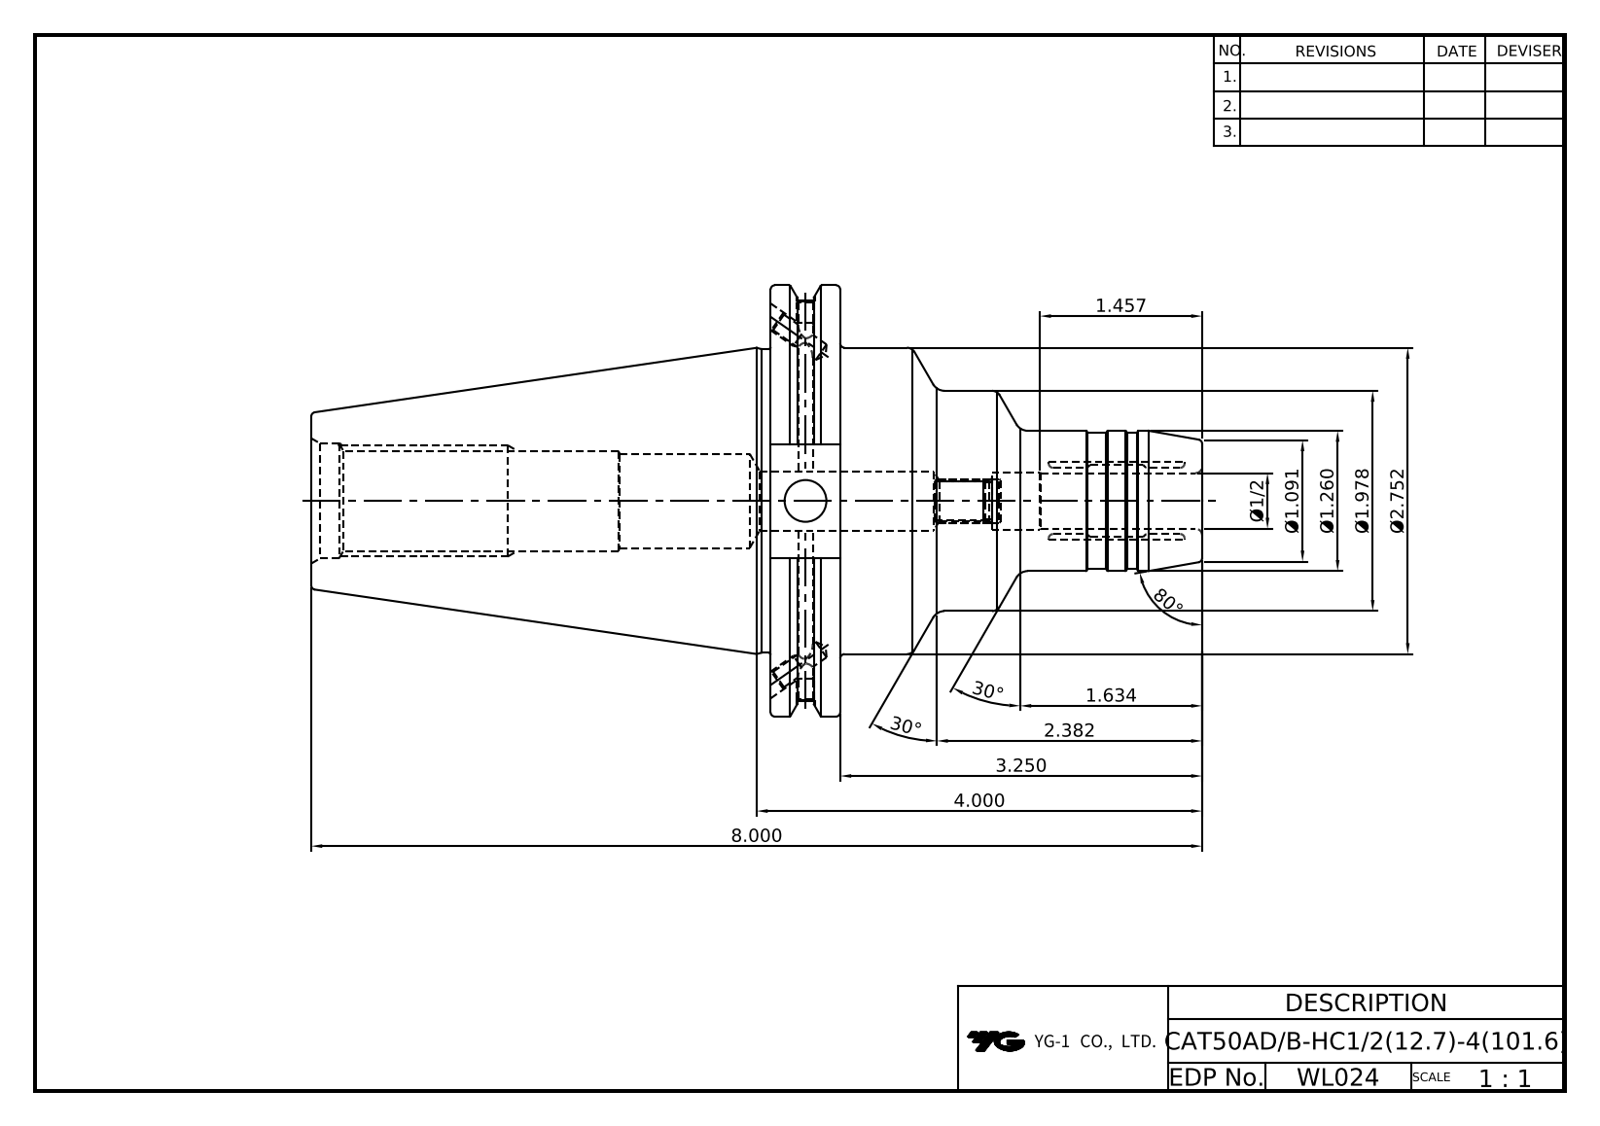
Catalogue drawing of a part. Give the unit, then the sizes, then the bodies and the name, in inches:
Units: inches
Overall size (bounding box): 8 × 3.875 × 3.728
Round holes (diameter × count): ⌀0.128 ×2, ⌀0.163 ×2, ⌀0.165 ×2, ⌀0.197 ×2, ⌀0.351 ×1, ⌀0.375 ×1, ⌀0.5 ×1, ⌀0.52 ×1, ⌀0.531 ×1, ⌀0.807 ×1, ⌀0.865 ×1, ⌀1.031 ×1
Round bosses / shafts (diameter × count): ⌀3.875 ×1, ⌀3.594 ×1, ⌀2.752 ×1, ⌀2.726 ×1, ⌀1.978 ×1, ⌀1.26 ×1, ⌀1.22 ×1
Main face-to-face distances: 0.625, 4.125, 4.75, 8, 3.875, 3.25, 2.875, 1.02, 4.363, 0.238
Volume: 28.02 in³ · Surface area: 89.51 in²
Bodies: 1 solid, 112 faces (37 planar, 34 cylindrical, 41 other)
Part name (STEP PRODUCT): LO-CAT50ADB-HC12.7-101.6
STEP written by: Autodesk Inventor 2020 (AUTOMOTIVE_DESIGN)
